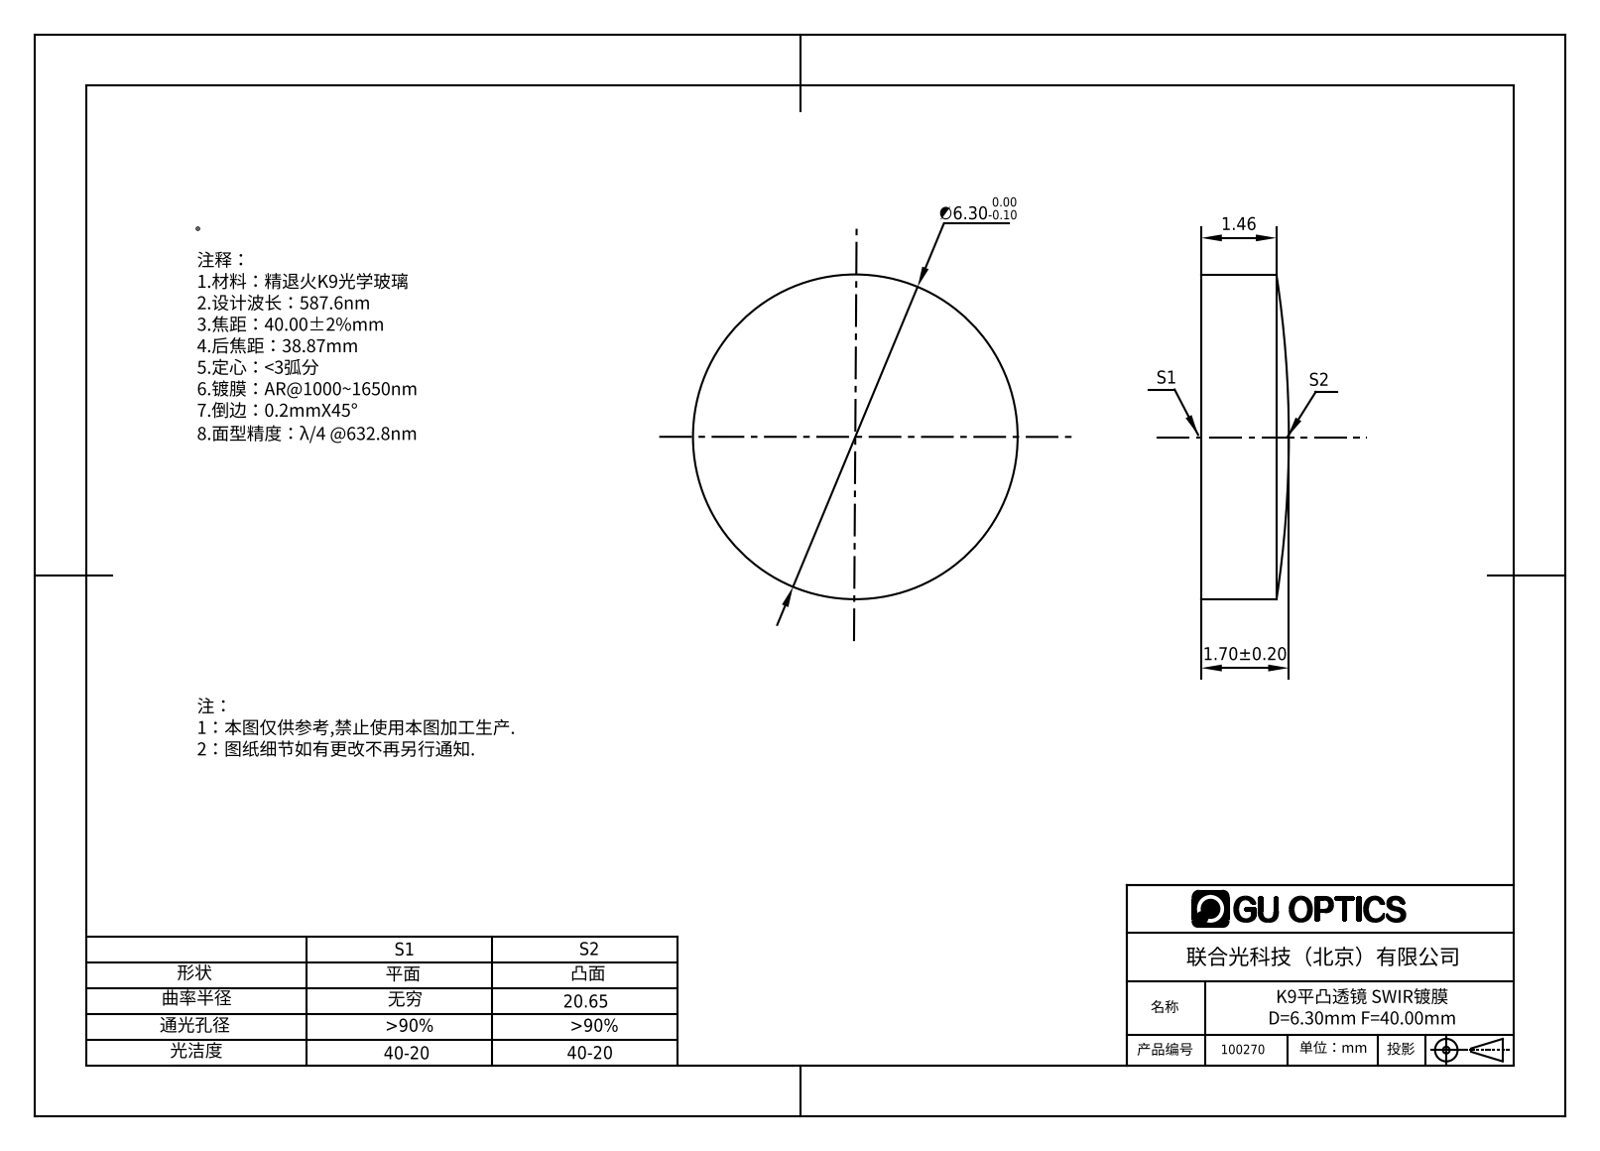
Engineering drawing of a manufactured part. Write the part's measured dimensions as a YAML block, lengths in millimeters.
part_name: "100098"
step_written_by: "SolidWorks 2016 (AUTOMOTIVE_DESIGN)"
units: millimeters
bodies: {solids: 1, faces: 5, planar: 1, cylindrical: 2, other: 2}
overall_size: [6.3, 6.3, 1.7]
volume: 49
surface_area: 91
round_bosses_or_shafts:
  - {diameter: 6.3, count: 1}
